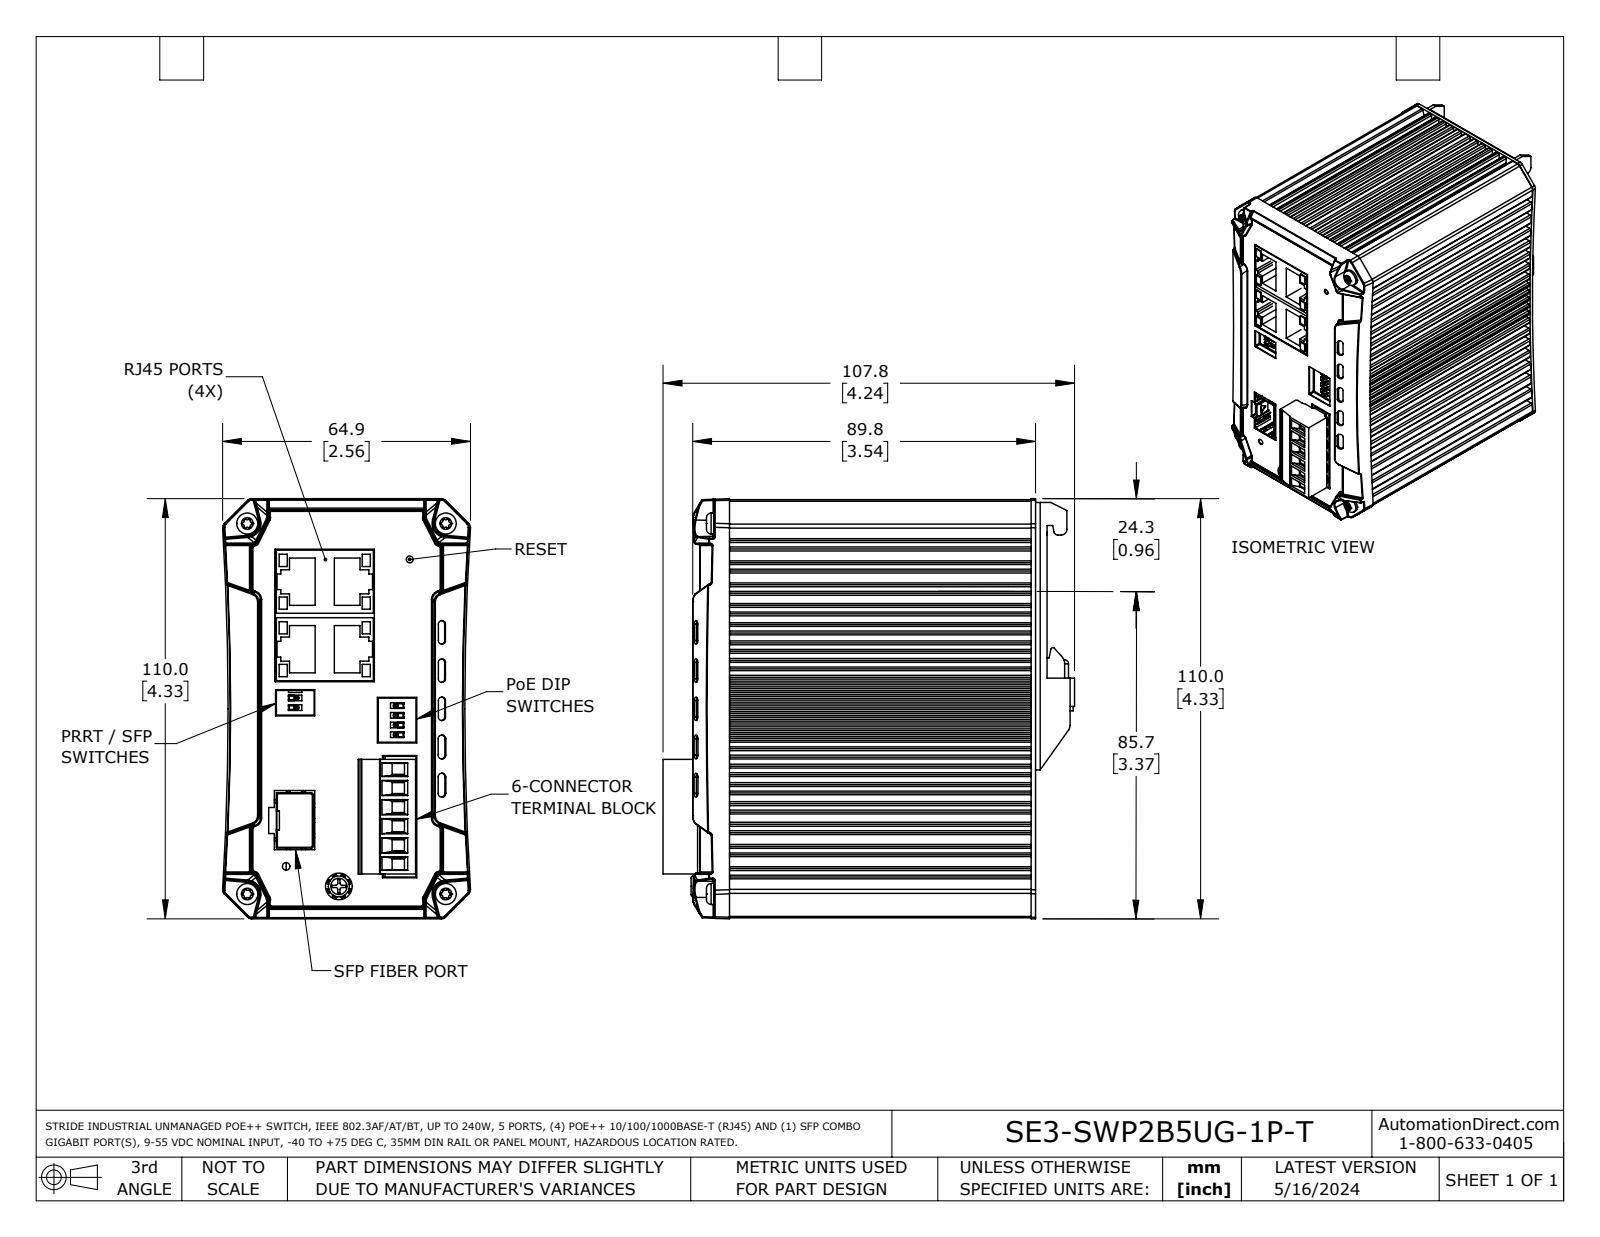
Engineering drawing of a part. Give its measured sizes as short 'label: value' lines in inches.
name: SE3-SWP2B5UG-1P-T_REV1
written by: SolidWorks 2023 (AUTOMOTIVE_DESIGN)
unit: in
bodies: 1 solid, 3037 faces (1434 planar, 1172 cylindrical, 431 other)
size: 4.331 × 4.244 × 2.556
volume: 33.37 in³; area: 146.9 in²
holes: 17× ⌀0.098, 15× ⌀0.157, 8× ⌀0.063, 6× ⌀0.138, 4× ⌀0.118, 1× ⌀0.071, 1× ⌀0.079, 1× ⌀0.276
bosses: 7× ⌀0.197, 6× ⌀0.149, 5× ⌀0.217, 5× ⌀0.118, 2× ⌀0.315, 2× ⌀0.205, 1× ⌀0.114
rounds: 276× R0.02, 202× R0.01, 73× R0.012, 72× R0.008, 47× R0.004, 38× R0.039, 25× R0.055, 24× R0.019
face distances: 0.087, 0.228, 0.285, 0.047, 3.157, 3.443, 2.925, 3.205, 3.49, 0.669
hole spacings: 0.394, 0.787, 1.024, 0.197, 0.354, 0.67, 1.378, 3.914
